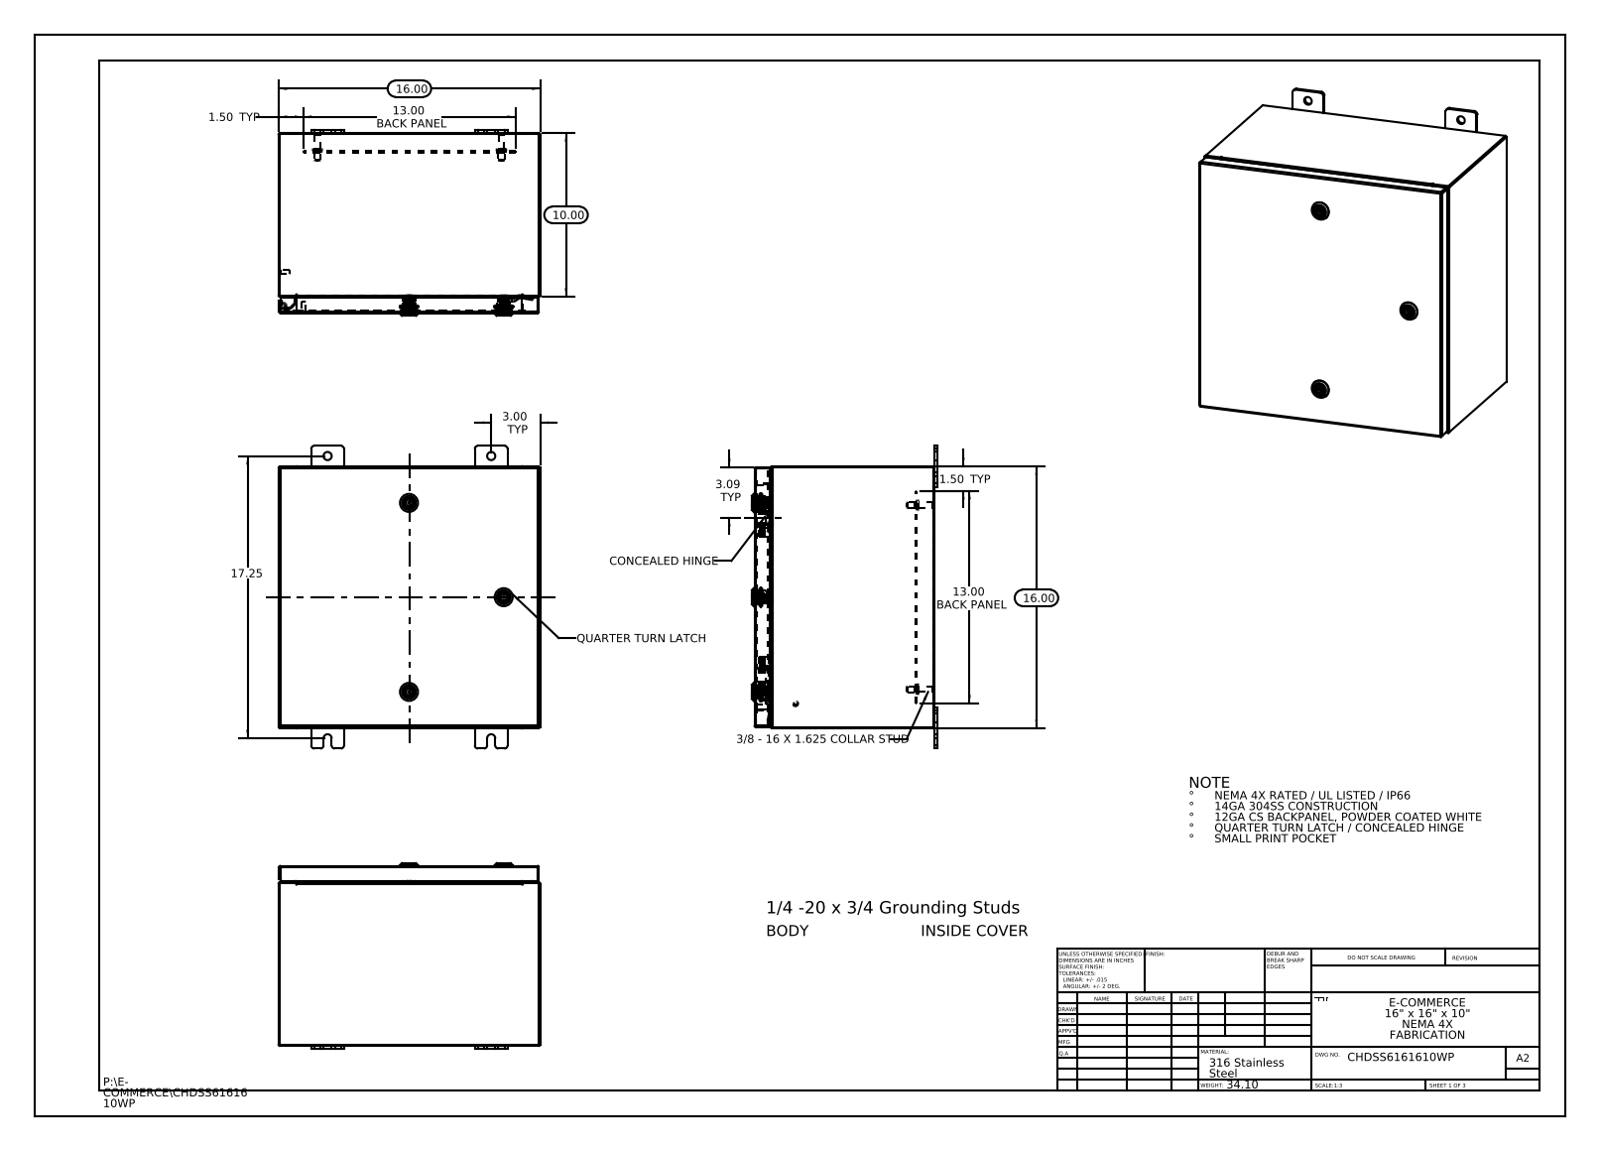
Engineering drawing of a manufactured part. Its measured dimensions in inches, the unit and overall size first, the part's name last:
Units: inches
Overall size (bounding box): 18.5 × 16 × 11.356
Round holes (diameter × count): ⌀0.5 ×8, ⌀0.136 ×4, ⌀0.197 ×3, ⌀0.394 ×3, ⌀0.4 ×3, ⌀0.63 ×3, ⌀0.787 ×3, ⌀0.211 ×1
Round bosses / shafts (diameter × count): ⌀0.236 ×5, ⌀0.625 ×4, ⌀0.375 ×4, ⌀0.33 ×4, ⌀1.102 ×3, ⌀0.78 ×3, ⌀0.626 ×3, ⌀0.61 ×3
Partial cylindrical surfaces — rounded edges, fillets, slot ends (radius × count): R0.006 ×99, R0.118 ×99, R0.028 ×36, R0.19 ×24, R0.013 ×18, R0.088 ×18, R0.02 ×12, R0.197 ×12
Main face-to-face distances: 0.075, 15.925, 0.074, 15.85, 16, 11.01, 10.935, 10.936, 10.861, 1
Hole centre spacings: 1.858, 3.065, 5.627, 10, 11.25, 11.25, 12.702, 13.015
Volume: 121.6 in³ · Surface area: 3 090 in²
Bodies: 37 solids, 2966 faces (938 planar, 930 cylindrical, 1098 other)
Part name (STEP PRODUCT): Nut-211301-IB-Industrilas_Nut-211301-IB-Industrilas; Washer-221320-IB-Industrilas_Washer-221320-IB-Industrilas; CHDSS6161610WP Cover; CHDSS6161610WP (+8 more)
STEP written by: SolidWorks 2013 (CONFIG_CONTROL_DESIGN)
